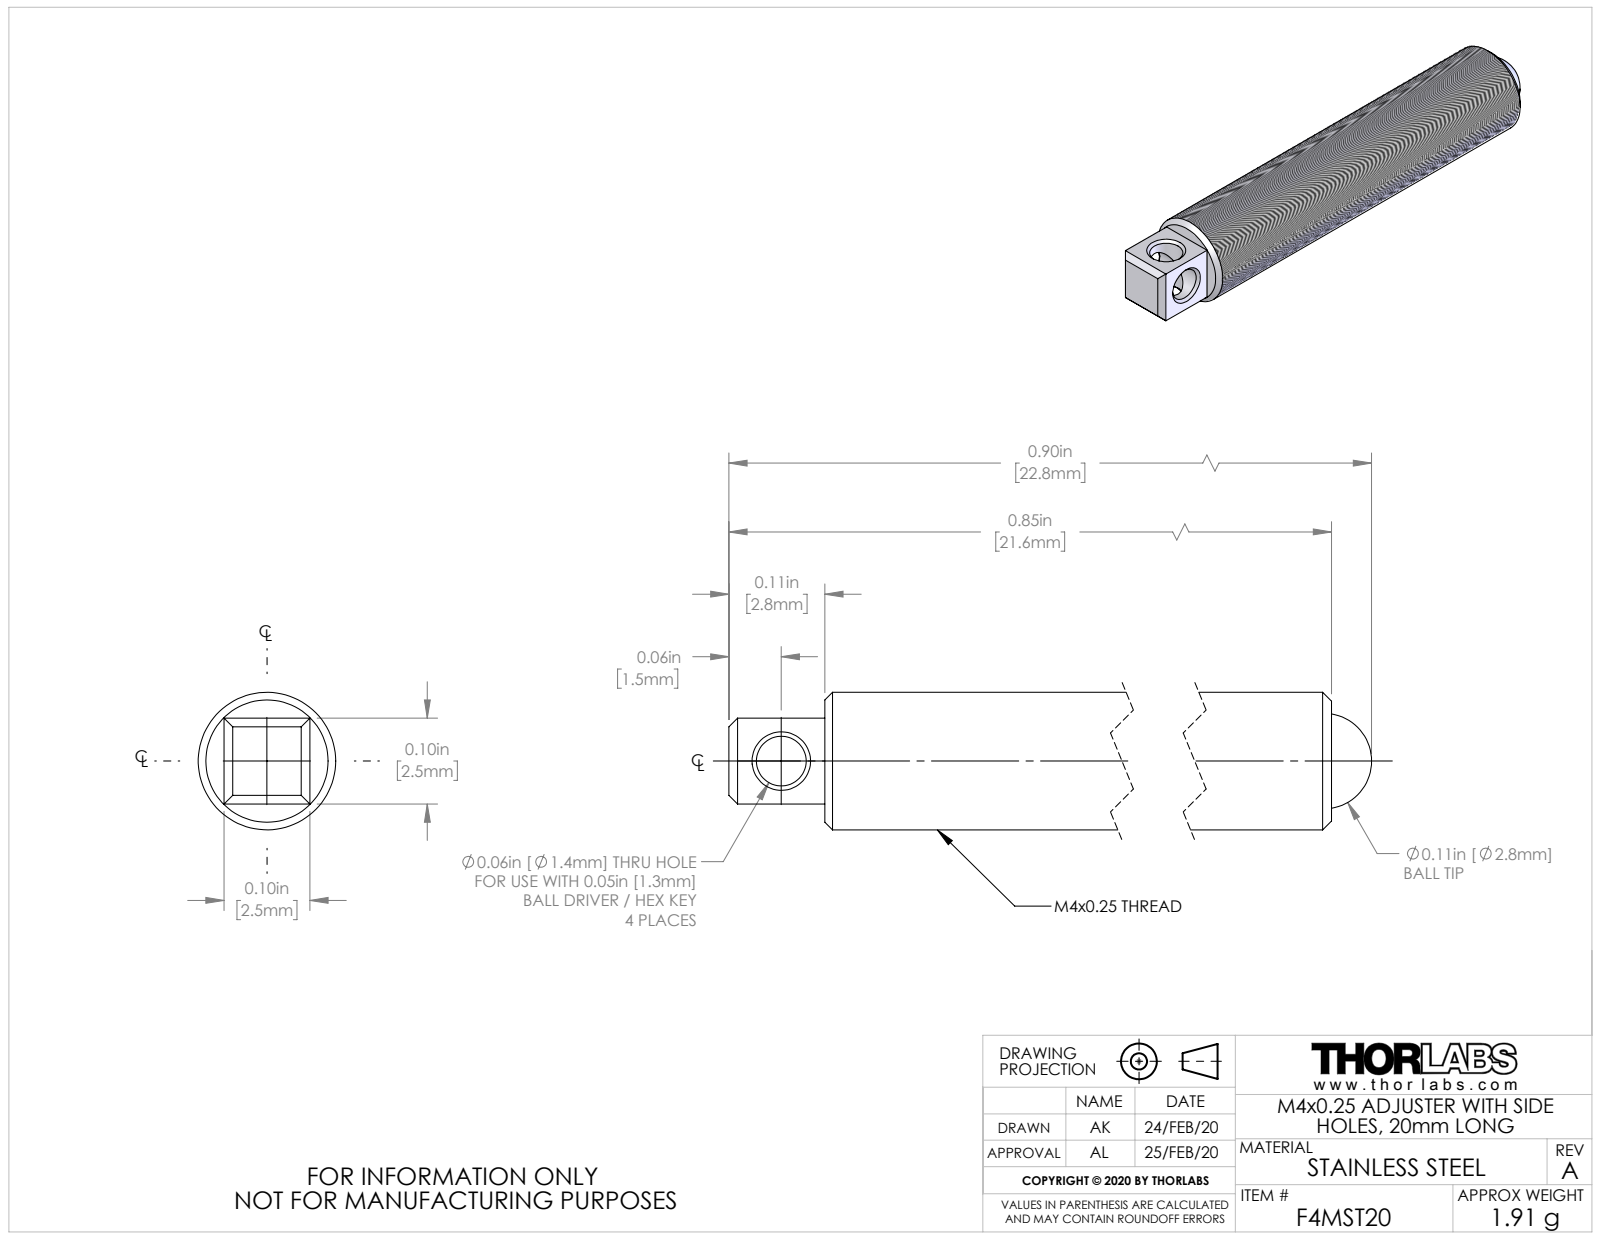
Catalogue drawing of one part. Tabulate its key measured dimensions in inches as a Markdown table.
| quantity | value |
| --- | --- |
| part name | TTN203603-E0W |
| STEP written by | SolidWorks 2018 (AUTOMOTIVE_DESIGN) |
| units | inches |
| bodies | 2 solids, 41 faces (11 planar, 12 cylindrical, 18 other) |
| overall size | 0.897 × 0.157 × 0.157 |
| volume | 0.015 in³ |
| surface area | 0.503 in² |
| round holes (diameter × count) | 0.057 × 2, 0.11 × 1 |
| round bosses / shafts (diameter × count) | 0.157 × 1 |
| main face-to-face distances | 0.098, 0.11, 0.742, 0.852 |
